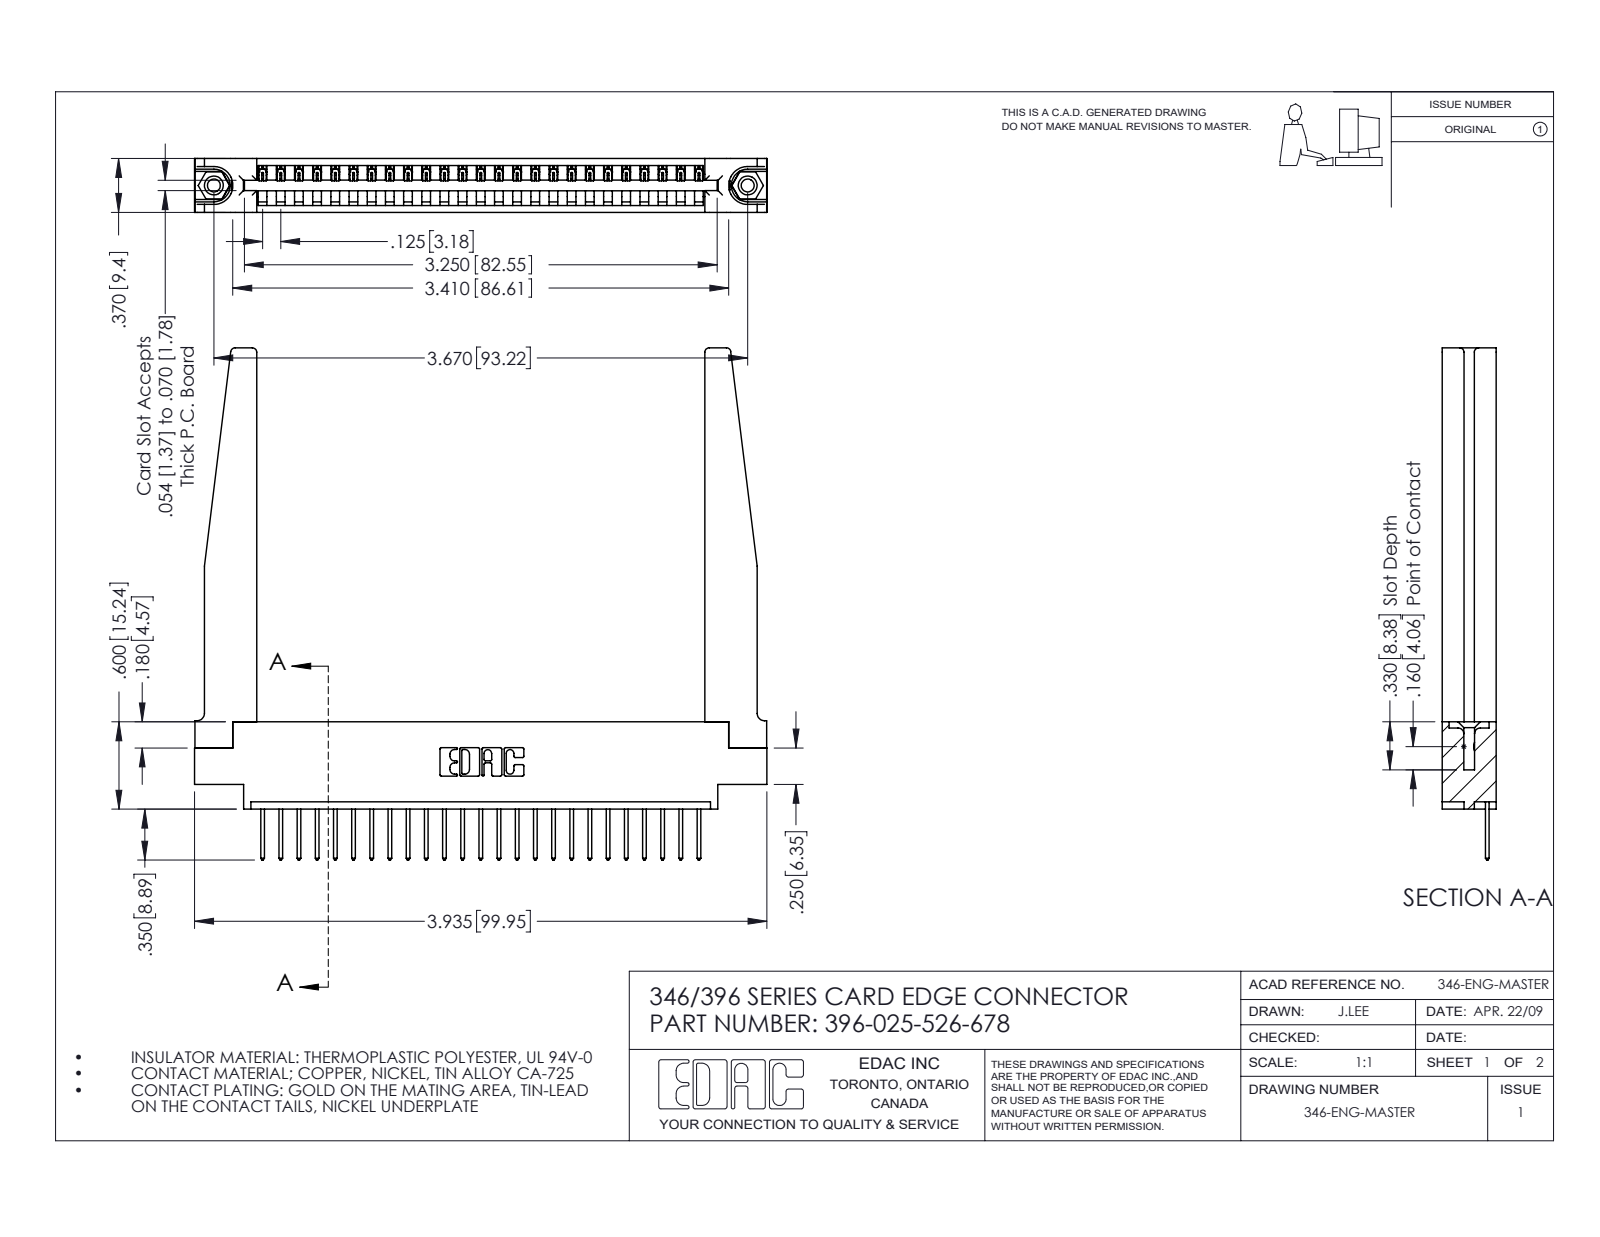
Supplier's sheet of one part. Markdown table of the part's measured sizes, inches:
| quantity | value |
| --- | --- |
| part name | 345-250-001_345-250-001-102; 396-025-526-678; 345-292-001_345-293-126; 346-220-078_345-220-078 (+1 more) |
| STEP written by | SolidWorks 2016 (CONFIG_CONTROL_DESIGN) |
| units | inches |
| bodies | 30 solids, 1810 faces (1222 planar, 536 cylindrical, 52 other) |
| overall size | 3.935 × 3.52 × 0.37 |
| volume | 0.988 in³ |
| surface area | 28.03 in² |
| round holes (diameter × count) | 0.089 × 2, 0.125 × 2, 0.156 × 2, 0.064 × 1 |
| round bosses / shafts (diameter × count) | 0.155 × 2 |
| partial cylindrical surfaces (radius × count) | 0.006 × 50, 0.01 × 50, 0.01 × 22, 0.03 × 8, 0.007 × 6, 0.031 × 6, 0.026 × 3, 0.031 × 2 |
| main face-to-face distances | 0.37, 0.048, 0.322, 0.072, 0.148, 0.15, 0.25, 0.298, 0.025, 0.222 |
| hole center spacings | 0.246, 3.462, 3.67 |
